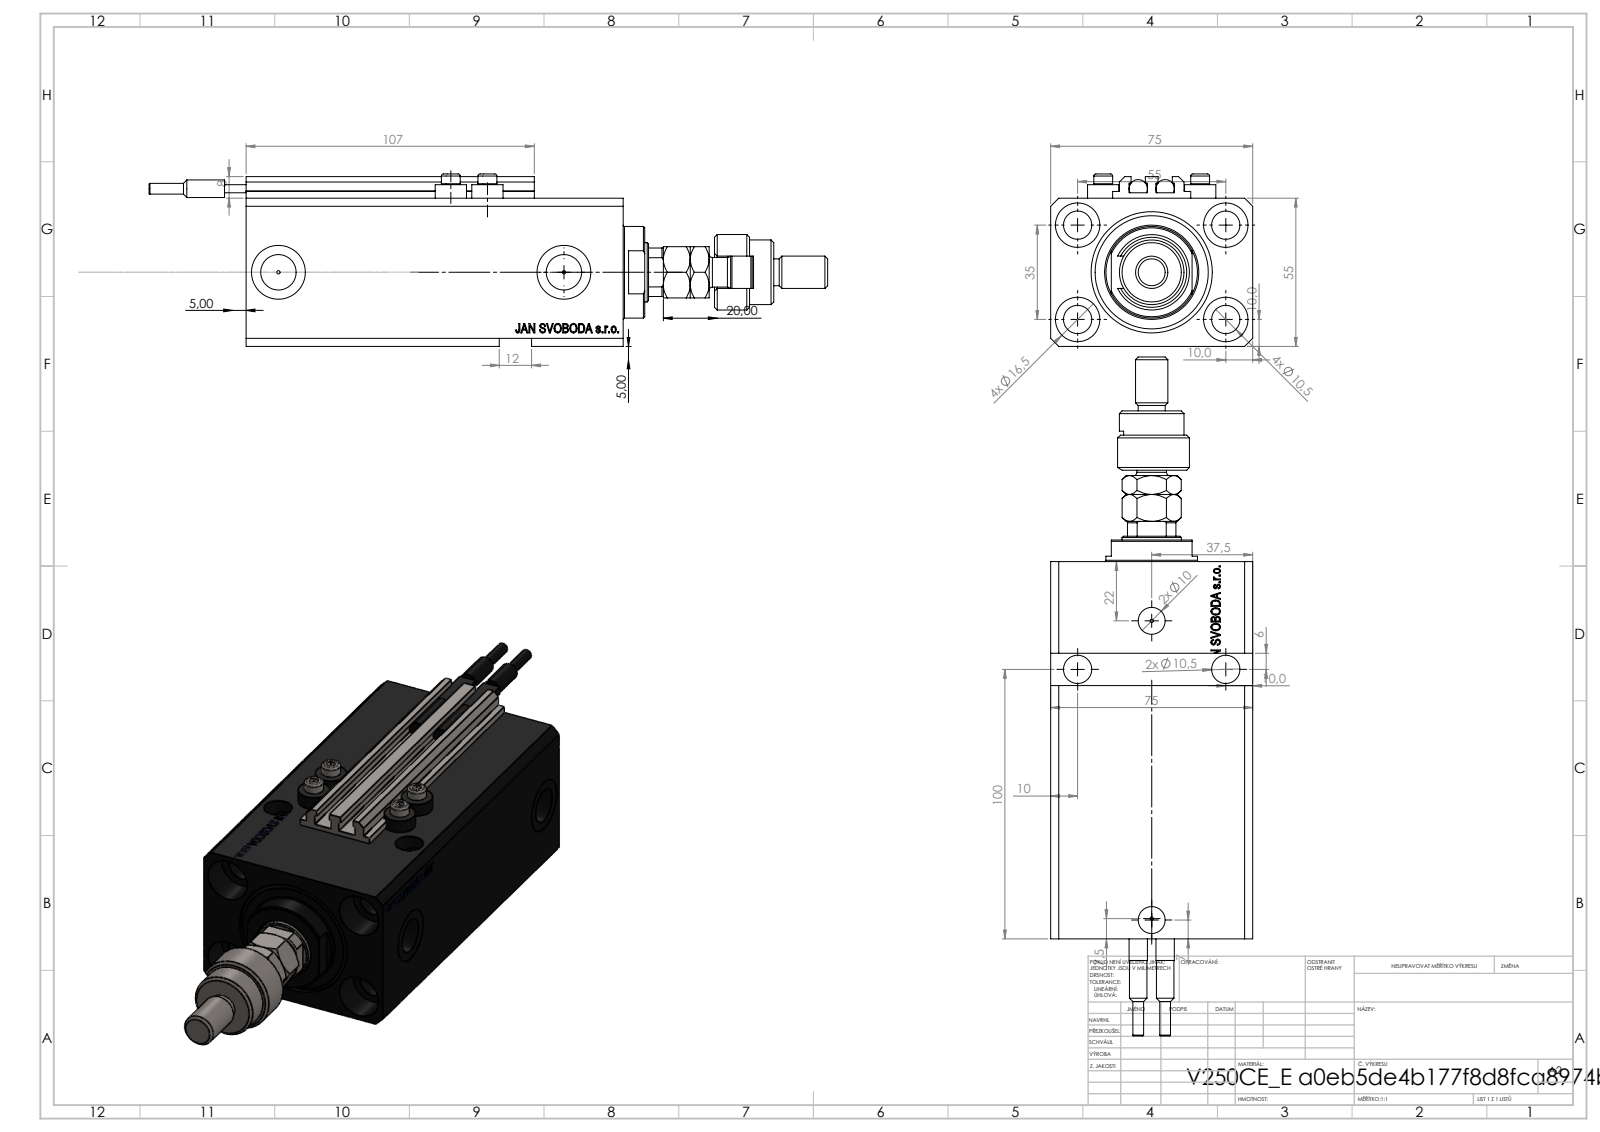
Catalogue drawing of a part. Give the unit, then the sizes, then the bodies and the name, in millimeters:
Units: millimetres
Overall size (bounding box): 252 × 75 × 64
Round holes (diameter × count): ⌀10.5 ×9, ⌀1.25 ×4, ⌀4 ×4, ⌀16.5 ×4, ⌀10 ×2, ⌀13.16 ×2, ⌀20 ×2, ⌀22 ×1, ⌀32 ×1, ⌀45 ×1
Round bosses / shafts (diameter × count): ⌀11.6 ×4, ⌀7 ×4, ⌀6.8 ×2, ⌀6.5 ×2, ⌀4 ×2, ⌀34 ×1, ⌀28 ×1, ⌀24 ×1
Partial cylindrical surfaces — rounded edges, fillets, slot ends (radius × count): R0.2 ×10, R9.75 ×1, R10.5 ×1
Main face-to-face distances: 55, 75, 15, 3, 57, 140, 9.9, 8, 125, 2
Hole centre spacings: 32.6, 32.87, 55, 96.98, 13.6, 14.09, 25.81, 32.58
Volume: 503 052 mm³ · Surface area: 126 323 mm²
Bodies: 12 solids, 1237 faces (578 planar, 183 cylindrical, 476 other)
Part name (STEP PRODUCT): FEMALE_PART_FOR_DFA; V250CE_C_VCP; MFA; ALLEN BOLT V250CE (+3 more)
STEP written by: SolidWorks 2019 (CONFIG_CONTROL_DESIGN)
